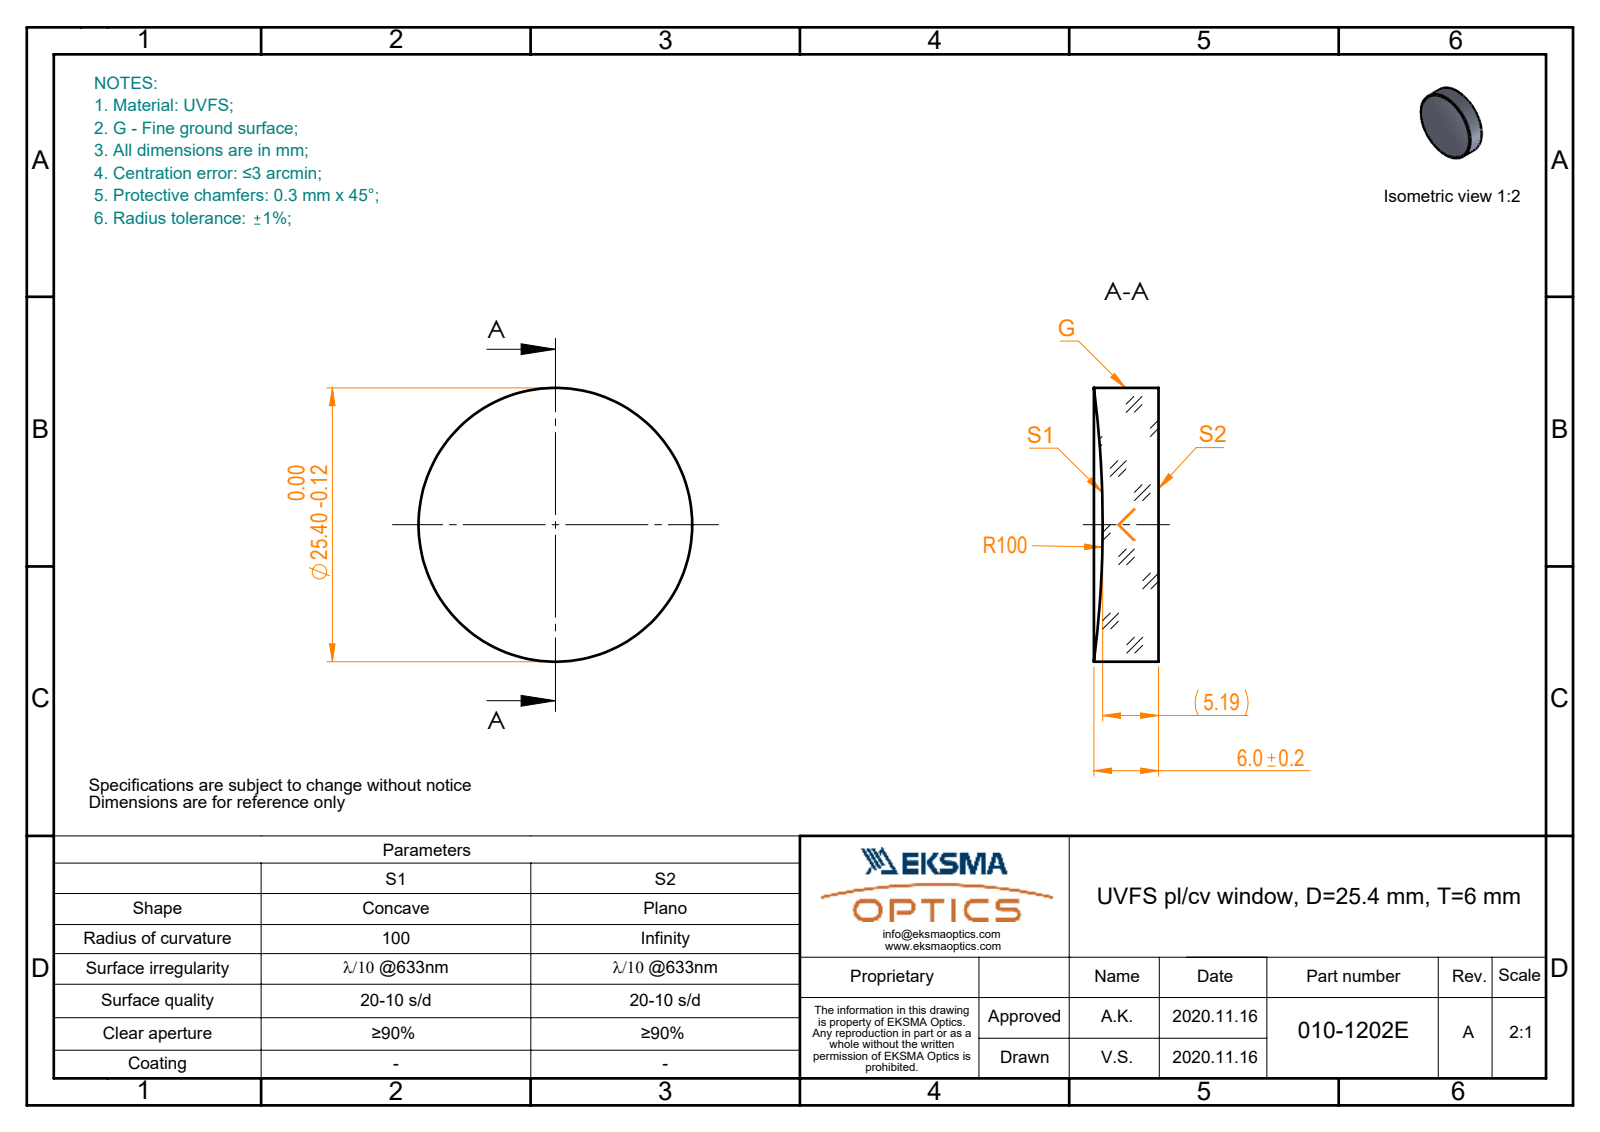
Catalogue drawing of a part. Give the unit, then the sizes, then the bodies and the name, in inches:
Units: inches
Overall size (bounding box): 1 × 1 × 0.236
Round bosses / shafts (diameter × count): ⌀1 ×1
Volume: 0.173 in³ · Surface area: 2.316 in²
Bodies: 1 solid, 5 faces (1 planar, 2 cylindrical, 2 other)
Part name (STEP PRODUCT): 010-1202E_UVFS_PCV_window
STEP written by: SolidWorks 2019 (CONFIG_CONTROL_DESIGN)
